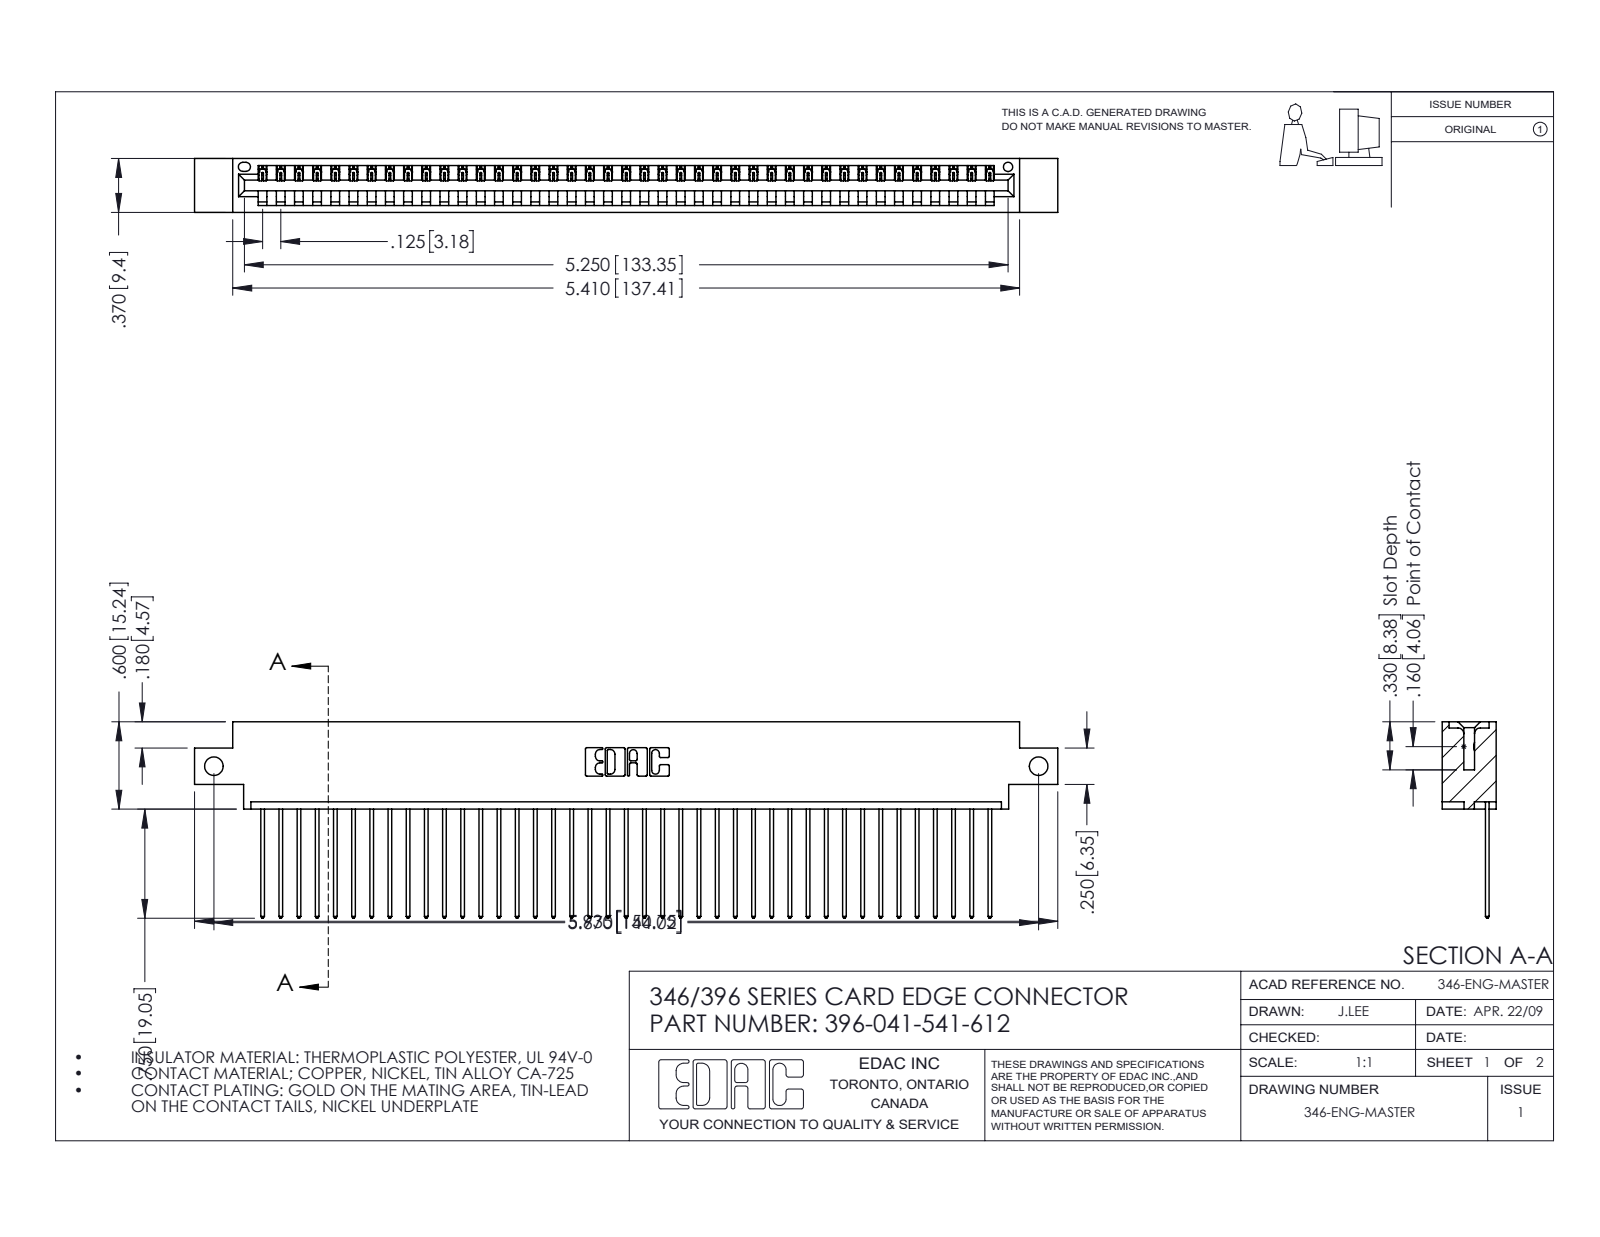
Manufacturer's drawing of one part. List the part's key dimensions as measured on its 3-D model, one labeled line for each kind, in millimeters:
Part name (STEP PRODUCT): 345-292-001_345-293-141; 346 Part_0.170 Offset - Side Mount; 396-041-541-612
STEP written by: SolidWorks 2016 (CONFIG_CONTROL_DESIGN)
Units: millimetres
Bodies: 42 solids, 2504 faces (1720 planar, 784 cylindrical, 0 other)
Overall size (bounding box): 150.7 × 34.3 × 9.4
Volume: 14 300 mm³ · Surface area: 18 700 mm²
Round holes (diameter × count): ⌀3.3 ×2, ⌀1.6 ×1
Partial cylindrical surfaces — rounded edges, fillets, slot ends (radius × count): R0.2 ×82, R0.3 ×82, R0.3 ×22, R0.2 ×6, R0.8 ×6, R0.7 ×3, R0.8 ×2, R1 ×2
Main face-to-face distances: 1.2, 8.2, 9.4, 6.4, 1.8, 7.6, 0.6, 3.8, 5.6, 2.5
Hole centre spacings: 144
